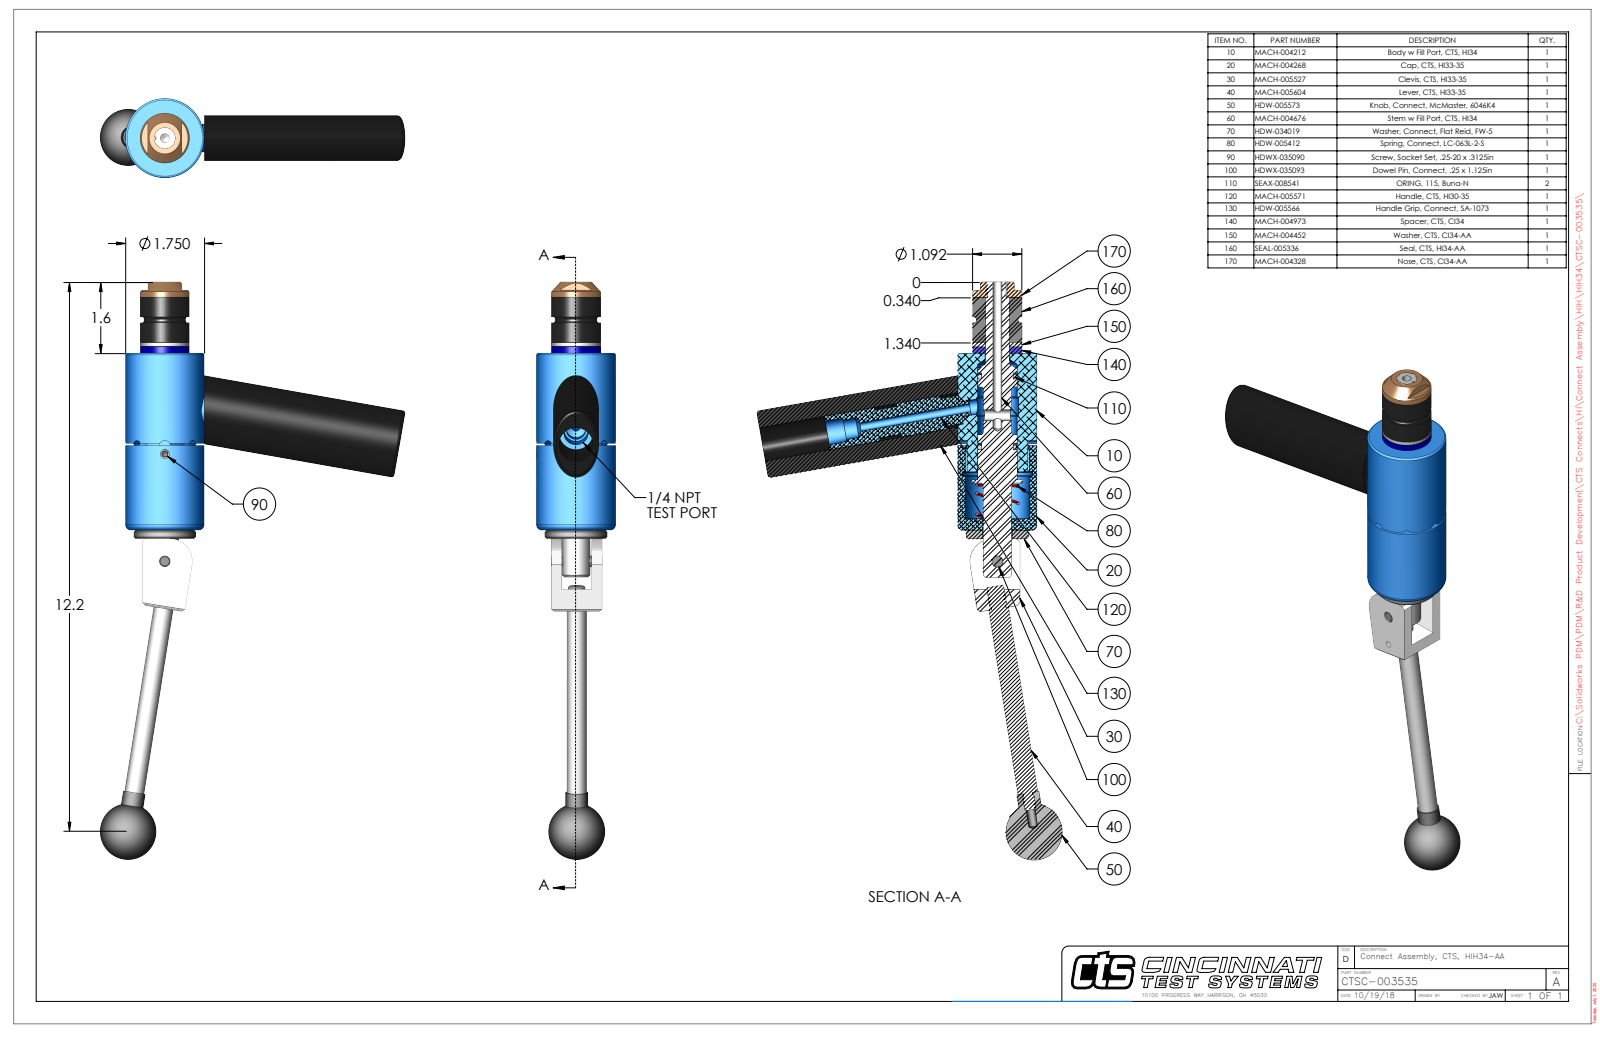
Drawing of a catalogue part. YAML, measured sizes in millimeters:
part_name: "CTSC-003535"
step_written_by: "SolidWorks 2023 (AUTOMOTIVE_DESIGN)"
units: millimeters
bodies: {solids: 11, faces: 309, planar: 109, cylindrical: 128, other: 72}
overall_size: [325, 171.8, 44.5]
volume: 297100
surface_area: 74580
round_holes:
  - {diameter: 5.1, count: 2}
  - {diameter: 3.8, count: 1}
  - {diameter: 4.7, count: 1}
  - {diameter: 5.2, count: 1}
  - {diameter: 6.3, count: 1}
  - {diameter: 6.4, count: 1}
  - {diameter: 6.4, count: 1}
  - {diameter: 8, count: 1}
  - {diameter: 10.7, count: 1}
  - {diameter: 11.1, count: 1}
  - {diameter: 13.5, count: 1}
  - {diameter: 13.7, count: 1}
round_bosses_or_shafts:
  - {diameter: 12.7, count: 2}
  - {diameter: 11.2, count: 2}
  - {diameter: 6.4, count: 2}
  - {diameter: 44.5, count: 1}
  - {diameter: 35.1, count: 1}
  - {diameter: 27.7, count: 1}
  - {diameter: 27.7, count: 1}
  - {diameter: 19.1, count: 1}
partial_cylinders:
  - {radius: 3.2, count: 4}
  - {radius: 0.7, count: 2}
  - {radius: 4.2, count: 1}
  - {radius: 4.2, count: 1}
  - {radius: 4.6, count: 1}
  - {radius: 8.4, count: 1}
  - {radius: 12.7, count: 1}
  - {radius: 17.7, count: 1}
face_to_face_distances: [99.6, 31.4, 131, 28.4, 25.4, 6, 105.6, 27.8, 2.4, 3.6]
hole_center_spacings: [18.8, 60.4, 79.1]
